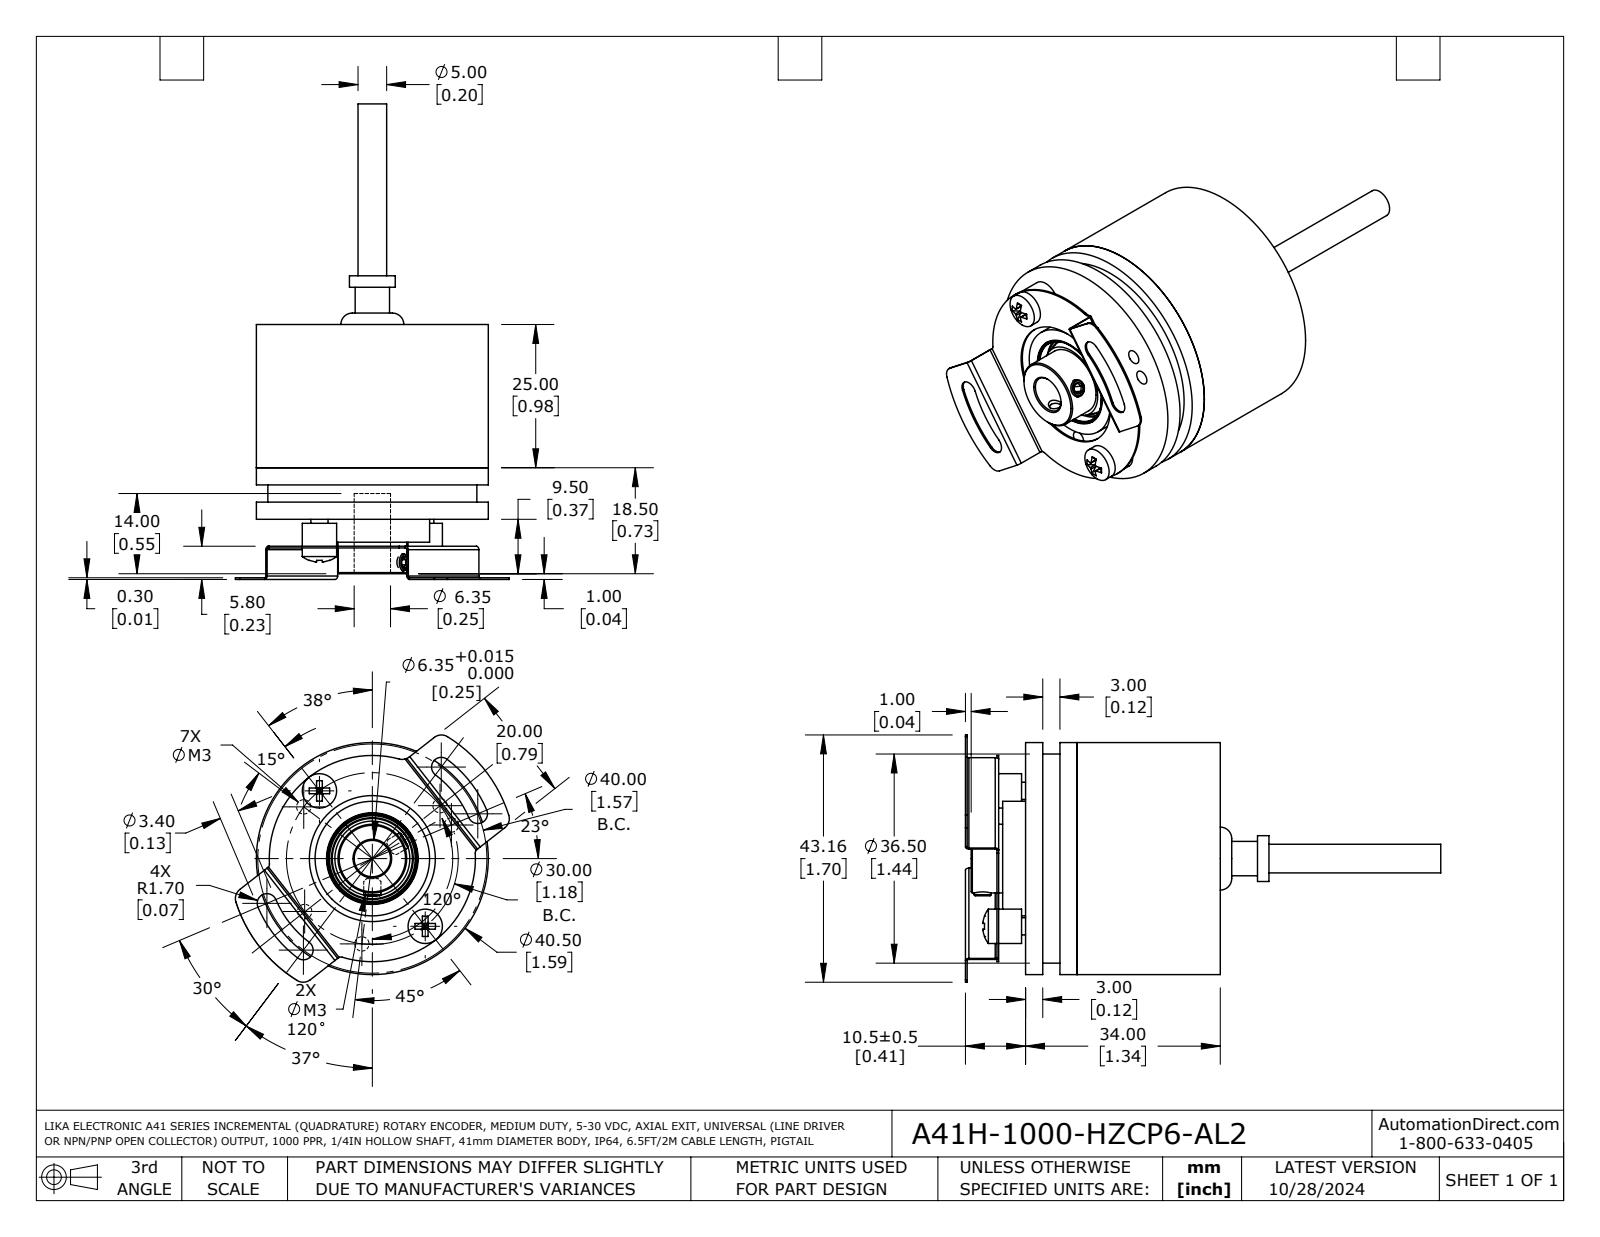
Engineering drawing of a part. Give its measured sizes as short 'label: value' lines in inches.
name: A41H-1000-HZCP6-AL2
written by: SolidWorks 2021 (AUTOMOTIVE_DESIGN)
unit: in
bodies: 15 solids, 465 faces (139 planar, 186 cylindrical, 140 other)
size: 3.268 × 1.883 × 1.699
volume: 1.187 in³; area: 32.38 in²
holes: 9× ⌀0.098, 7× ⌀0.063, 3× ⌀0.157, 2× ⌀0.087, 2× ⌀0.126, 2× ⌀0.138, 1× ⌀0.169, 1× ⌀0.25, 1× ⌀0.295, 1× ⌀0.512, 1× ⌀0.602, 1× ⌀0.612
bosses: 4× ⌀0.118, 3× ⌀0.236, 2× ⌀0.15, 2× ⌀0.079, 1× ⌀1.594, 1× ⌀1.496, 1× ⌀1.457, 1× ⌀1.437
rounds: 14× R0.039, 8× R0.008, 5× R0.079, 4× R0.012, 4× R0.024, 4× R0.067, 3× R0.03, 1× R0.709
face distances: 0.118, 0.433, 1.339, 0.906, 0.197, 1.22, 0.079, 0.866, 0.039, 0.787
hole spacings: 0.591, 0.669, 0.835, 0.11, 0.118, 0.837, 0.945, 1.023
